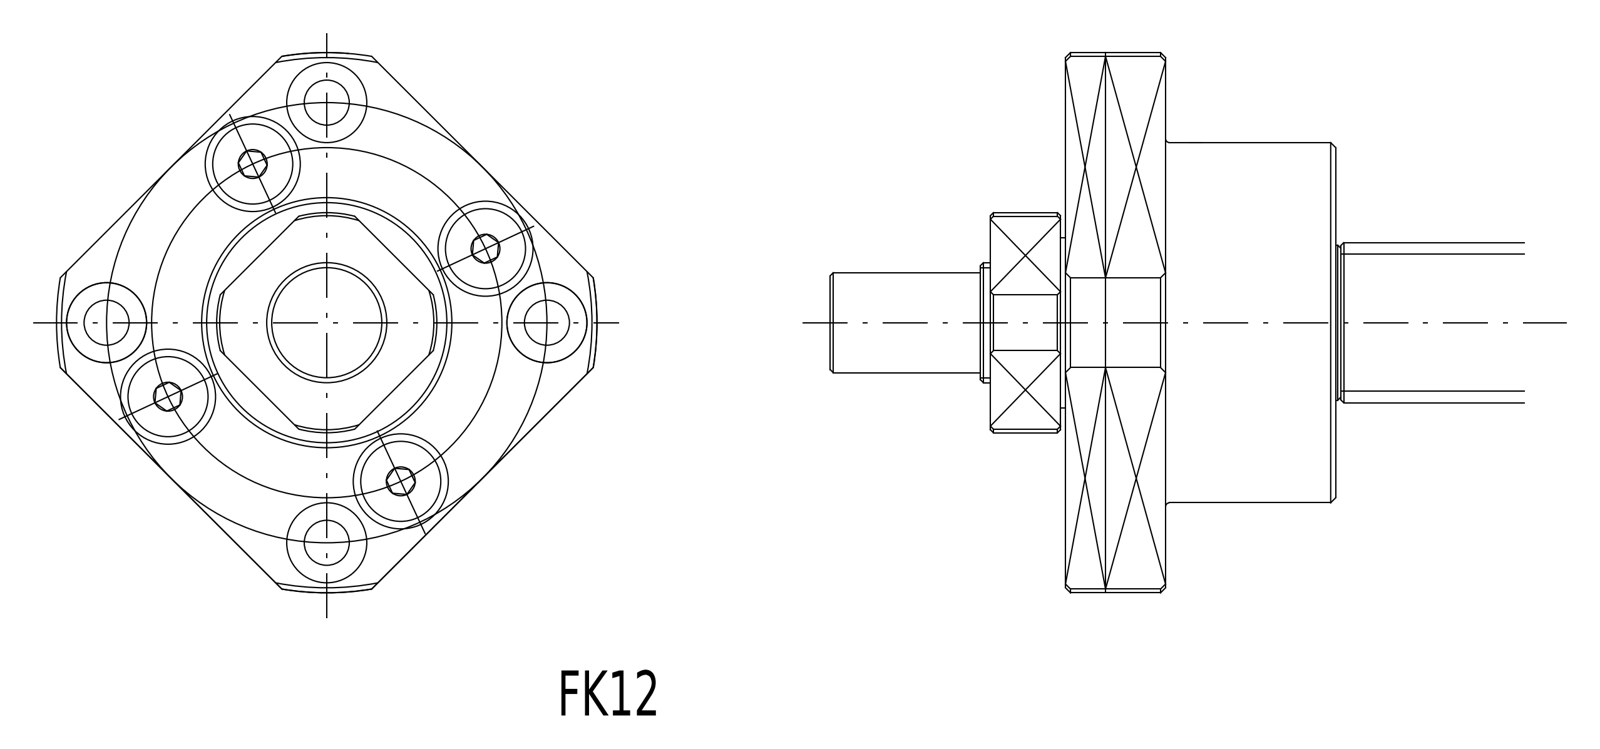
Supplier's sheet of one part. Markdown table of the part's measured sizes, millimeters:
| quantity | value |
| --- | --- |
| STEP written by | SolidWorks 2008 (CONFIG_CONTROL_DESIGN) |
| units | millimeters |
| bodies | 35 solids, 448 faces (66 planar, 130 cylindrical, 252 other) |
| overall size | 44 × 44 × 35 |
| volume | 27 668 mm³ |
| surface area | 23 362 mm² |
| round holes (diameter × count) | 4.5 × 8, 3.3 × 6, 8 × 4, 11 × 1, 12 × 1, 16 × 1, 22.6 × 1, 24 × 1, 25 × 1 |
| round bosses / shafts (diameter × count) | 36 × 1, 35.4 × 1, 28 × 1, 22 × 1, 18 × 1, 17.4 × 1, 16.5 × 1, 15.4 × 1 |
| partial cylindrical surfaces (radius × count) | 27 × 1 |
| main face-to-face distances | 4, 6, 10, 8, 0.5, 44, 21.5, 27, 23, 5 |
| hole center spacings | 9.5, 18, 21.76, 22.01, 25.45, 31.12, 33.8, 39.06 |
